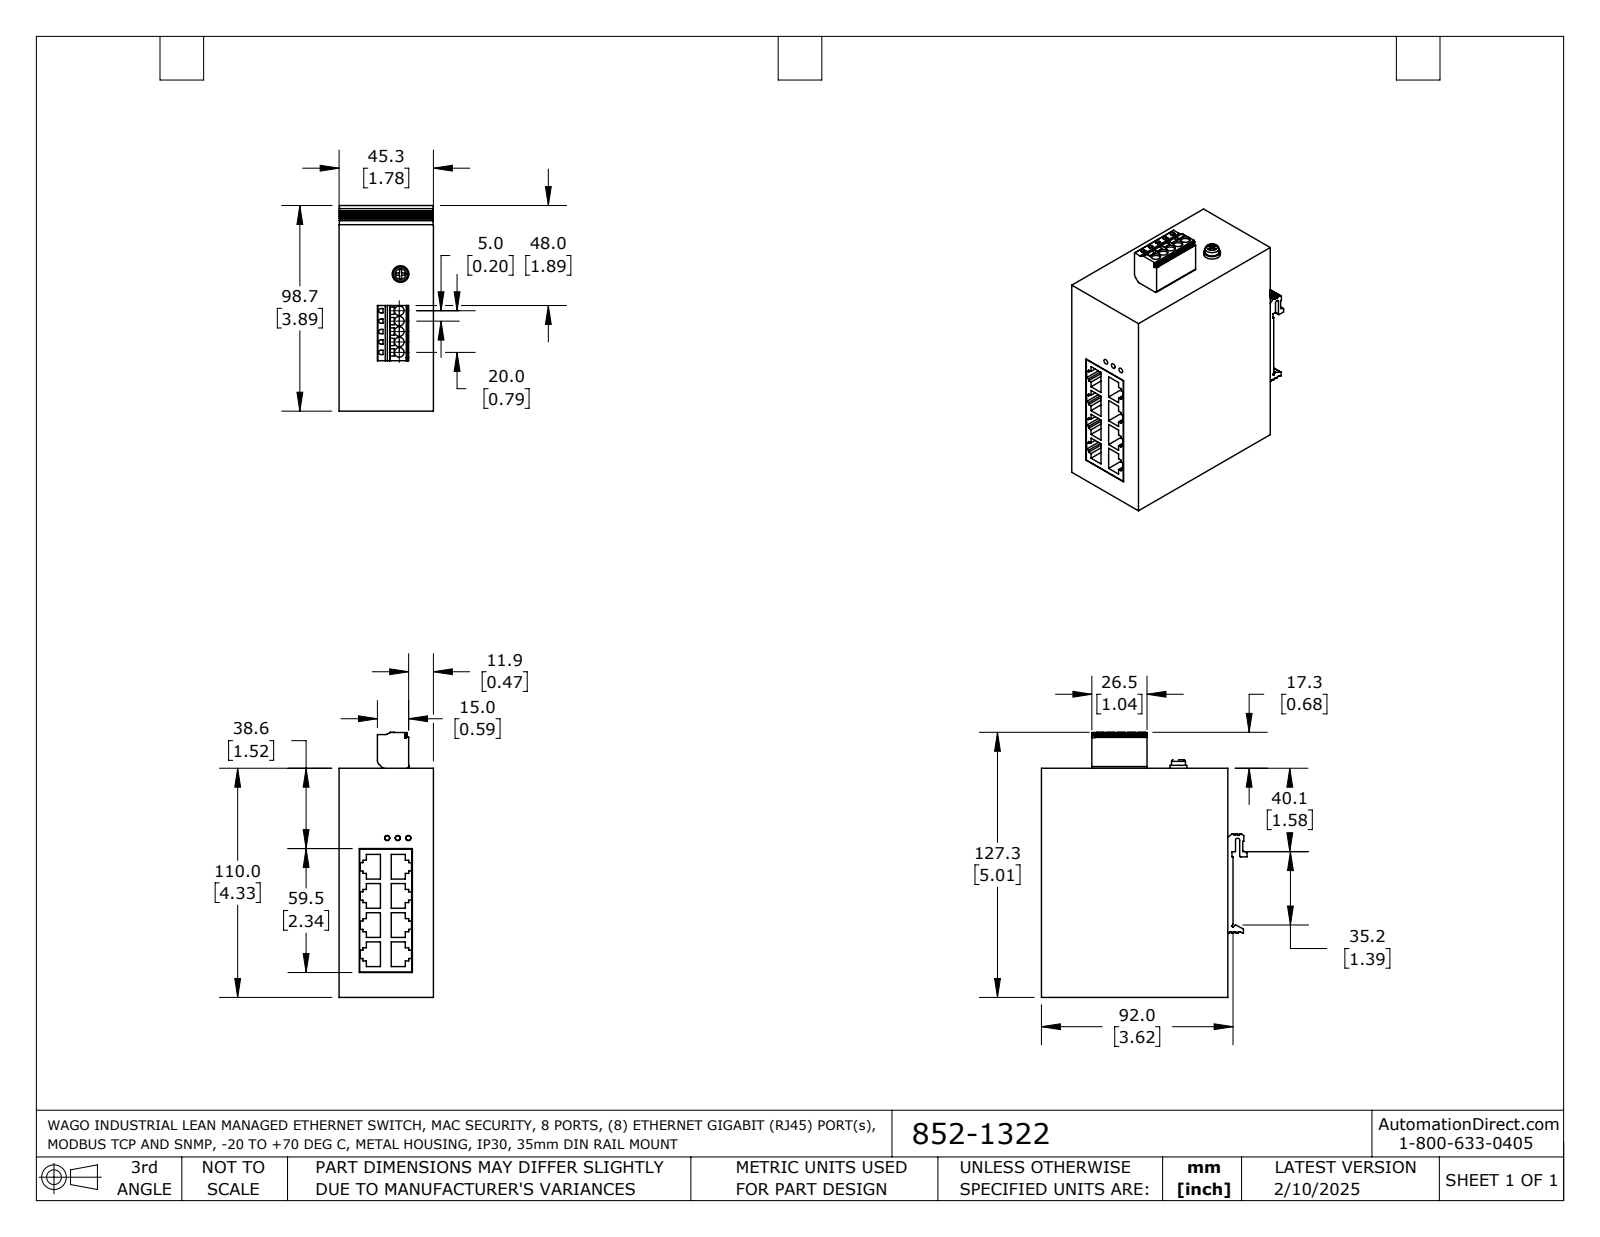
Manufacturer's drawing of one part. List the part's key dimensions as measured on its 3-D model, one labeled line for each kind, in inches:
Part name (STEP PRODUCT): 852-1322
STEP written by: SolidWorks 2021 (AUTOMOTIVE_DESIGN)
Units: inches
Bodies: 1 solid, 349 faces (256 planar, 88 cylindrical, 5 other)
Overall size (bounding box): 5.01 × 3.886 × 1.783
Volume: 27.51 in³ · Surface area: 73.6 in²
Round holes (diameter × count): ⌀0.181 ×5, ⌀0.098 ×3
Round bosses / shafts (diameter × count): ⌀0.315 ×1, ⌀0.264 ×1
Partial cylindrical surfaces — rounded edges, fillets, slot ends (radius × count): R0.004 ×46, R0.041 ×5, R0.02 ×4, R0.008 ×3, R0.031 ×1, R0.039 ×1, R0.047 ×1, R0.079 ×1
Main face-to-face distances: 1.783, 4.331, 3.524, 0.098, 3.622, 0.551, 0.467, 0.205, 3.157, 3.059
Hole centre spacings: 0.197, 0.394, 0.2, 0.591, 0.4, 0.787
